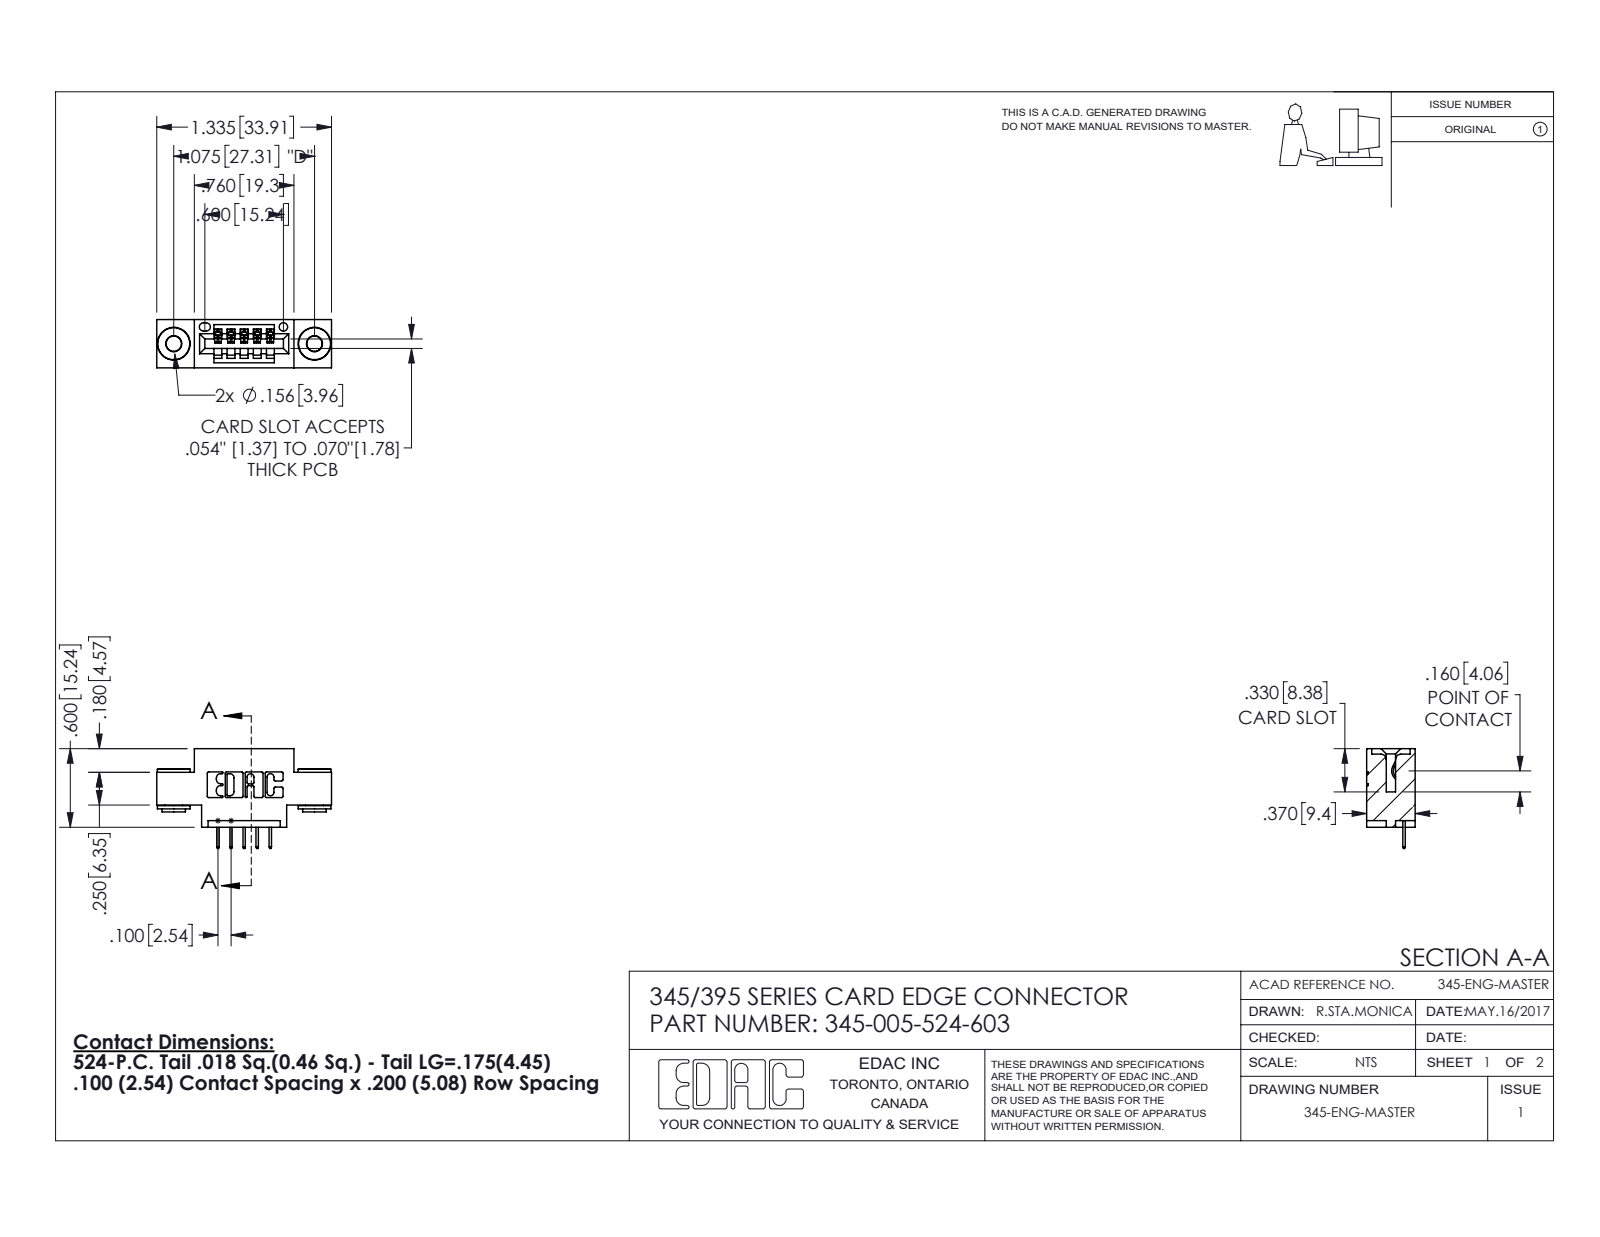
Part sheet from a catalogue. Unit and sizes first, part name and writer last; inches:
Units: inches
Overall size (bounding box): 1.335 × 0.762 × 0.37
Round holes (diameter × count): ⌀0.116 ×2, ⌀0.156 ×2, ⌀0.064 ×1
Round bosses / shafts (diameter × count): ⌀0.25 ×2, ⌀0.18 ×2, ⌀0.136 ×2
Partial cylindrical surfaces — rounded edges, fillets, slot ends (radius × count): R0.01 ×22, R0.006 ×10, R0.007 ×6, R0.031 ×6, R0.026 ×3, R0.031 ×2, R0.04 ×2, R0.014 ×1
Main face-to-face distances: 0.37, 0.2, 0.1, 0.072, 0.298, 0.25, 0.025, 0.06, 0.55, 0.255
Hole centre spacings: 0.27, 0.847, 1.075
Volume: 0.171 in³ · Surface area: 5.427 in²
Bodies: 8 solids, 478 faces (324 planar, 146 cylindrical, 8 other)
Part name (STEP PRODUCT): 345-292-001_345-293-124; 345-250-002_345-250-002-102; 345-005-524-603; 345 Part_0.170 Offset - 0.156 Dia-TH
STEP written by: SolidWorks 2016 (CONFIG_CONTROL_DESIGN)
